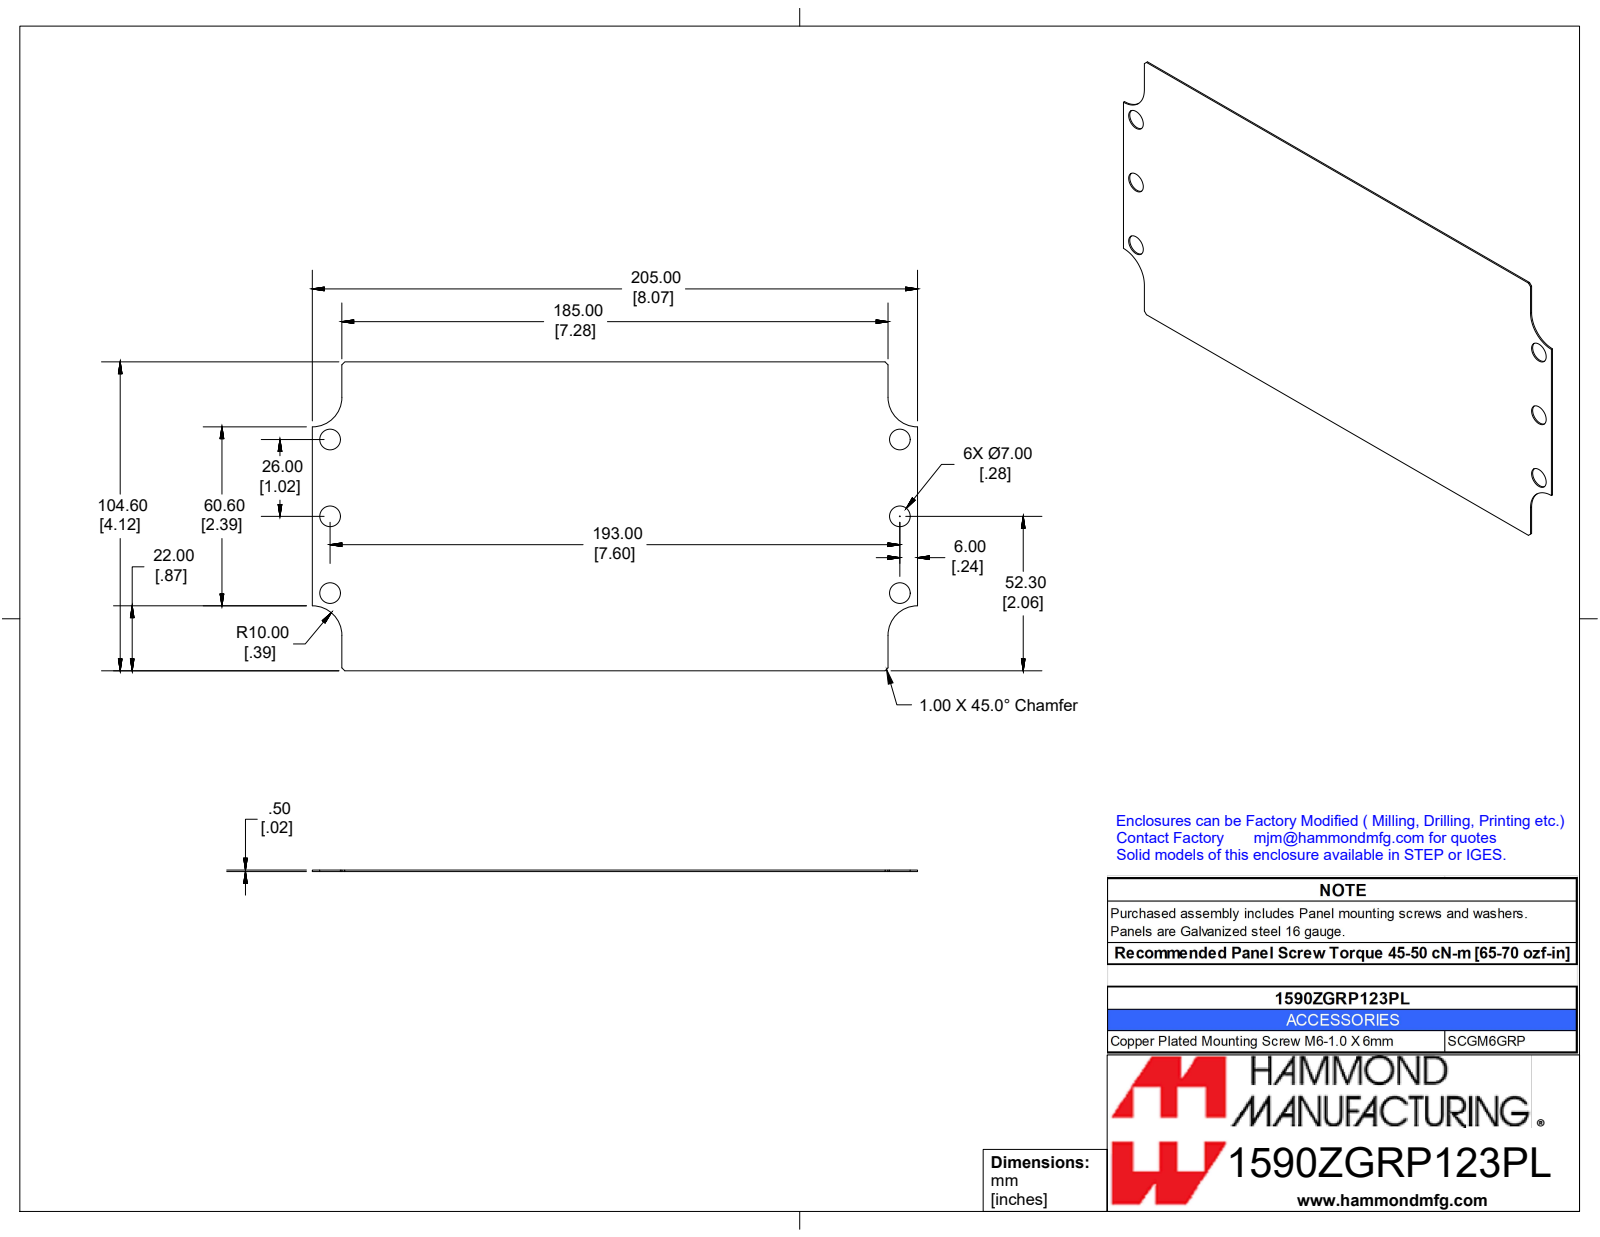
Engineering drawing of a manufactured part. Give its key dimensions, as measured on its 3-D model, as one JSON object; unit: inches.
{"part_name": "1590ZGRP123PL", "step_written_by": "SolidWorks 2019 (CONFIG_CONTROL_DESIGN)", "units": "inches", "bodies": {"solids": 1, "faces": 24, "planar": 14, "cylindrical": 10, "other": 0}, "overall_size": [8.071, 4.118, 0.02], "volume_in3": 0.623, "surface_area_in2": 63.86, "round_holes": [[0.276, 6]], "partial_cylinders_radius": [[0.394, 4]], "face_to_face_distances": [0.02, 4.118, 8.071, 0.394, 7.677, 7.283, 8.005, 8.006], "hole_center_spacings": [1.024, 7.667, 7.598, 2.047, 7.869]}
